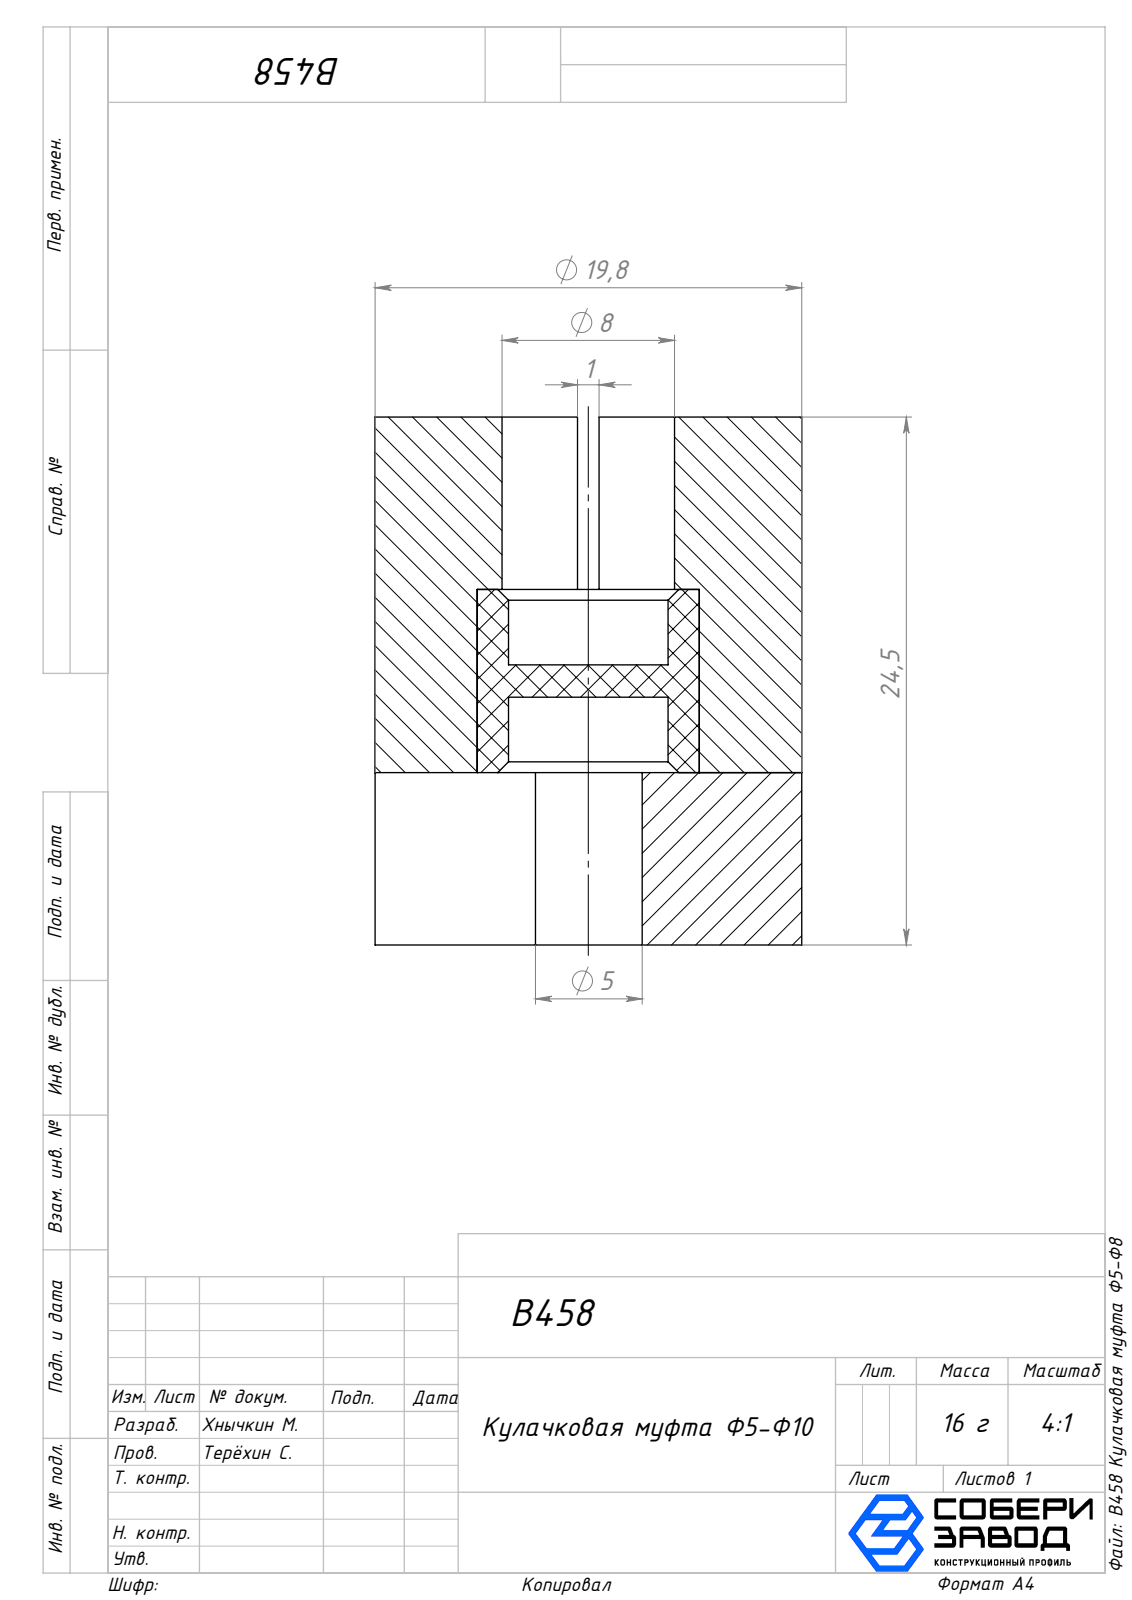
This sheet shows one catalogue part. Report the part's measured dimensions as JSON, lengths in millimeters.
{"part_name": "B458 Кулачковая муфта Ф5-Ф8; Верх_00; Низ_00; Середина_00", "step_written_by": "SolidWorks 2025 (AUTOMOTIVE_DESIGN)", "units": "millimeters", "bodies": {"solids": 3, "faces": 56, "planar": 24, "cylindrical": 28, "other": 4}, "overall_size": [24.5, 19.8, 19.8], "volume_mm3": 6571, "surface_area_mm2": 4525, "round_holes": [[5, 1], [7.4, 1], [8, 1]], "round_bosses_or_shafts": [[19.8, 1]], "partial_cylinders_radius": [[6, 8]], "face_to_face_distances": [8, 16.5, 8.5, 24.5, 4.65, 5.65, 1, 11.5, 13, 3.5]}
